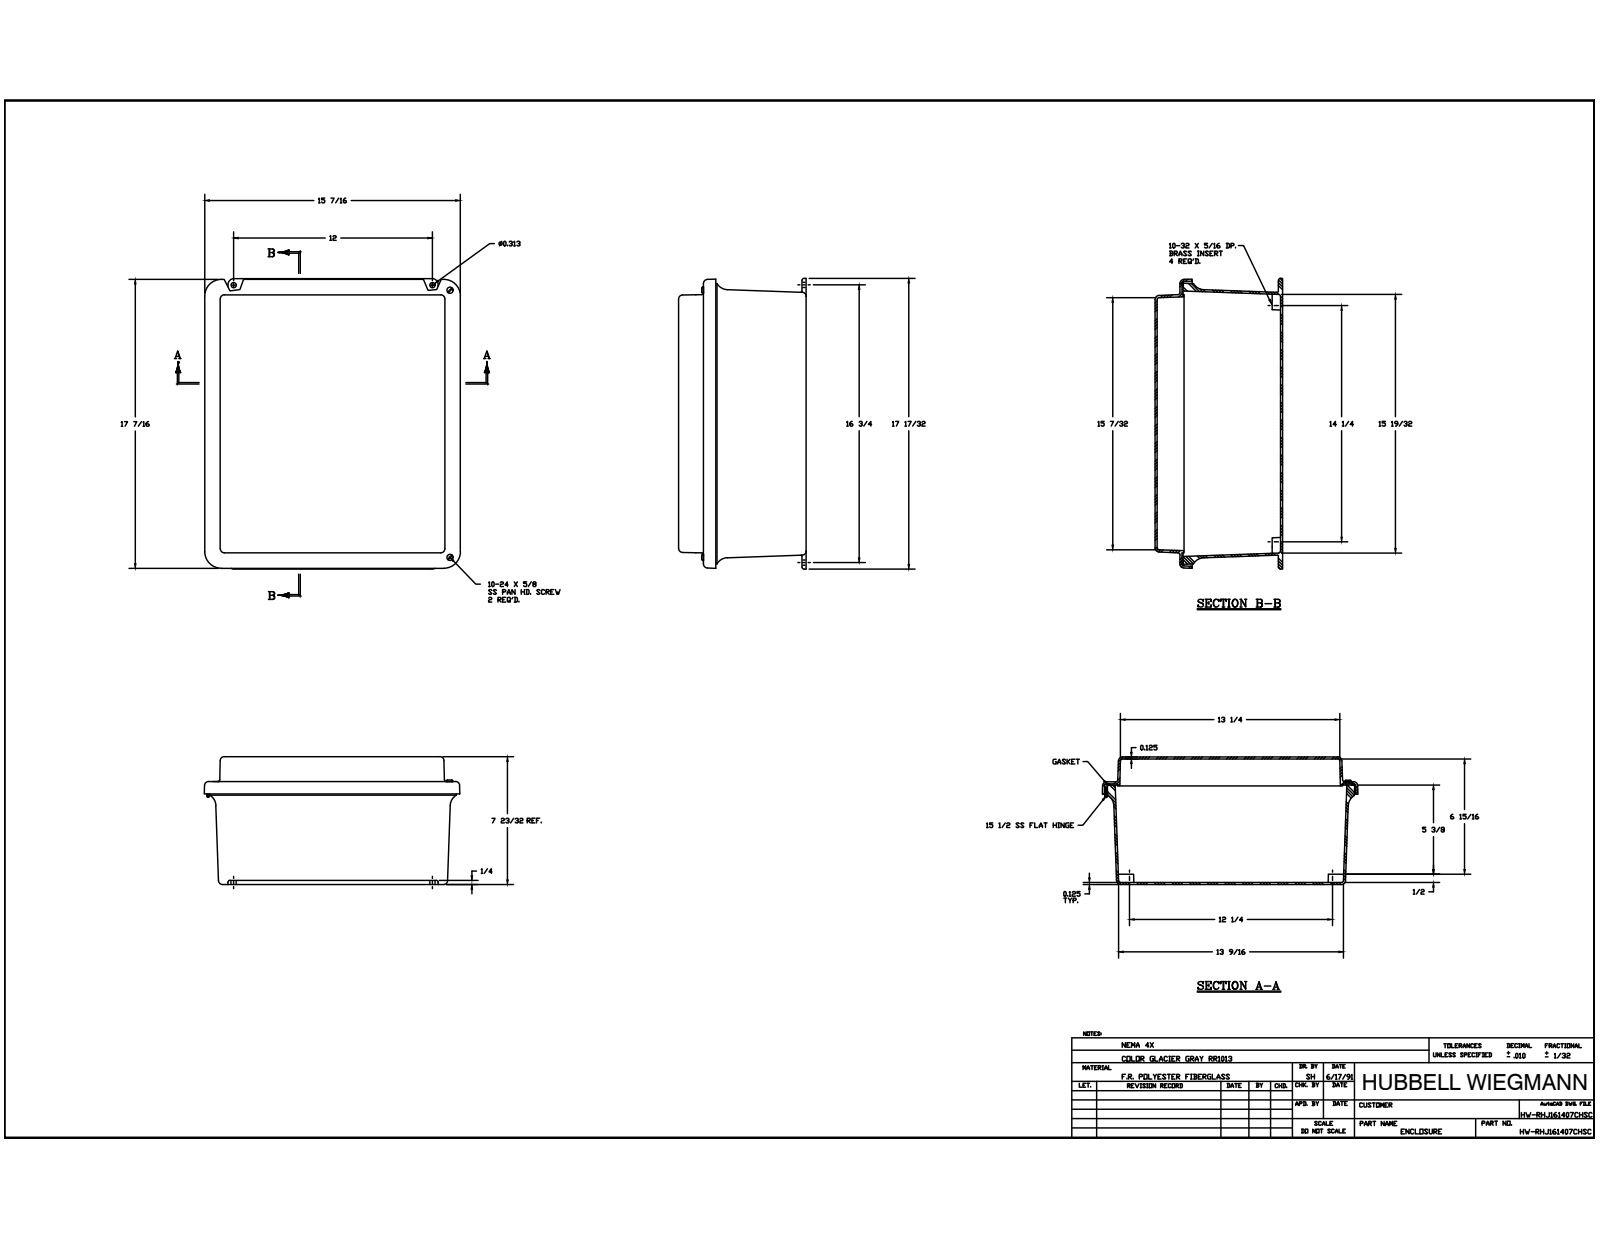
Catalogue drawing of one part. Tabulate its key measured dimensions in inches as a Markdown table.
| quantity | value |
| --- | --- |
| part name | J1614HW_3; RMINS45821P_115; RMINS45821P_116; RMINS45821P_117 (+8 more) |
| STEP written by | Autodesk Inventor 2014 (AUTOMOTIVE_DESIGN) |
| units | inches |
| bodies | 24 solids, 965 faces (364 planar, 370 cylindrical, 231 other) |
| overall size | 17.531 × 15.454 × 7.697 |
| volume | 146.8 in³ |
| surface area | 2 102 in² |
| round holes (diameter × count) | 0.131 × 10, 0.14 × 10, 0.152 × 8, 0.156 × 4, 0.218 × 4, 0.145 × 2, 0.085 × 1 |
| round bosses / shafts (diameter × count) | 0.25 × 10, 0.125 × 10, 0.27 × 6, 0.19 × 2, 0.156 × 2, 0.155 × 1 |
| partial cylindrical surfaces (radius × count) | 0.031 × 20, 0.125 × 20, 0.25 × 20, 0.2 × 4, 0.297 × 4, 0.375 × 4, 0.75 × 4, 0.063 × 2 |
| main face-to-face distances | 0.125, 0.125, 7.447, 7.697, 7.572, 7.572, 1.502, 5.945, 6.07, 1.627 |
| hole center spacings | 3.75, 7.5, 11.25, 0.25, 3.5, 1.321, 7.25, 13.22 |
